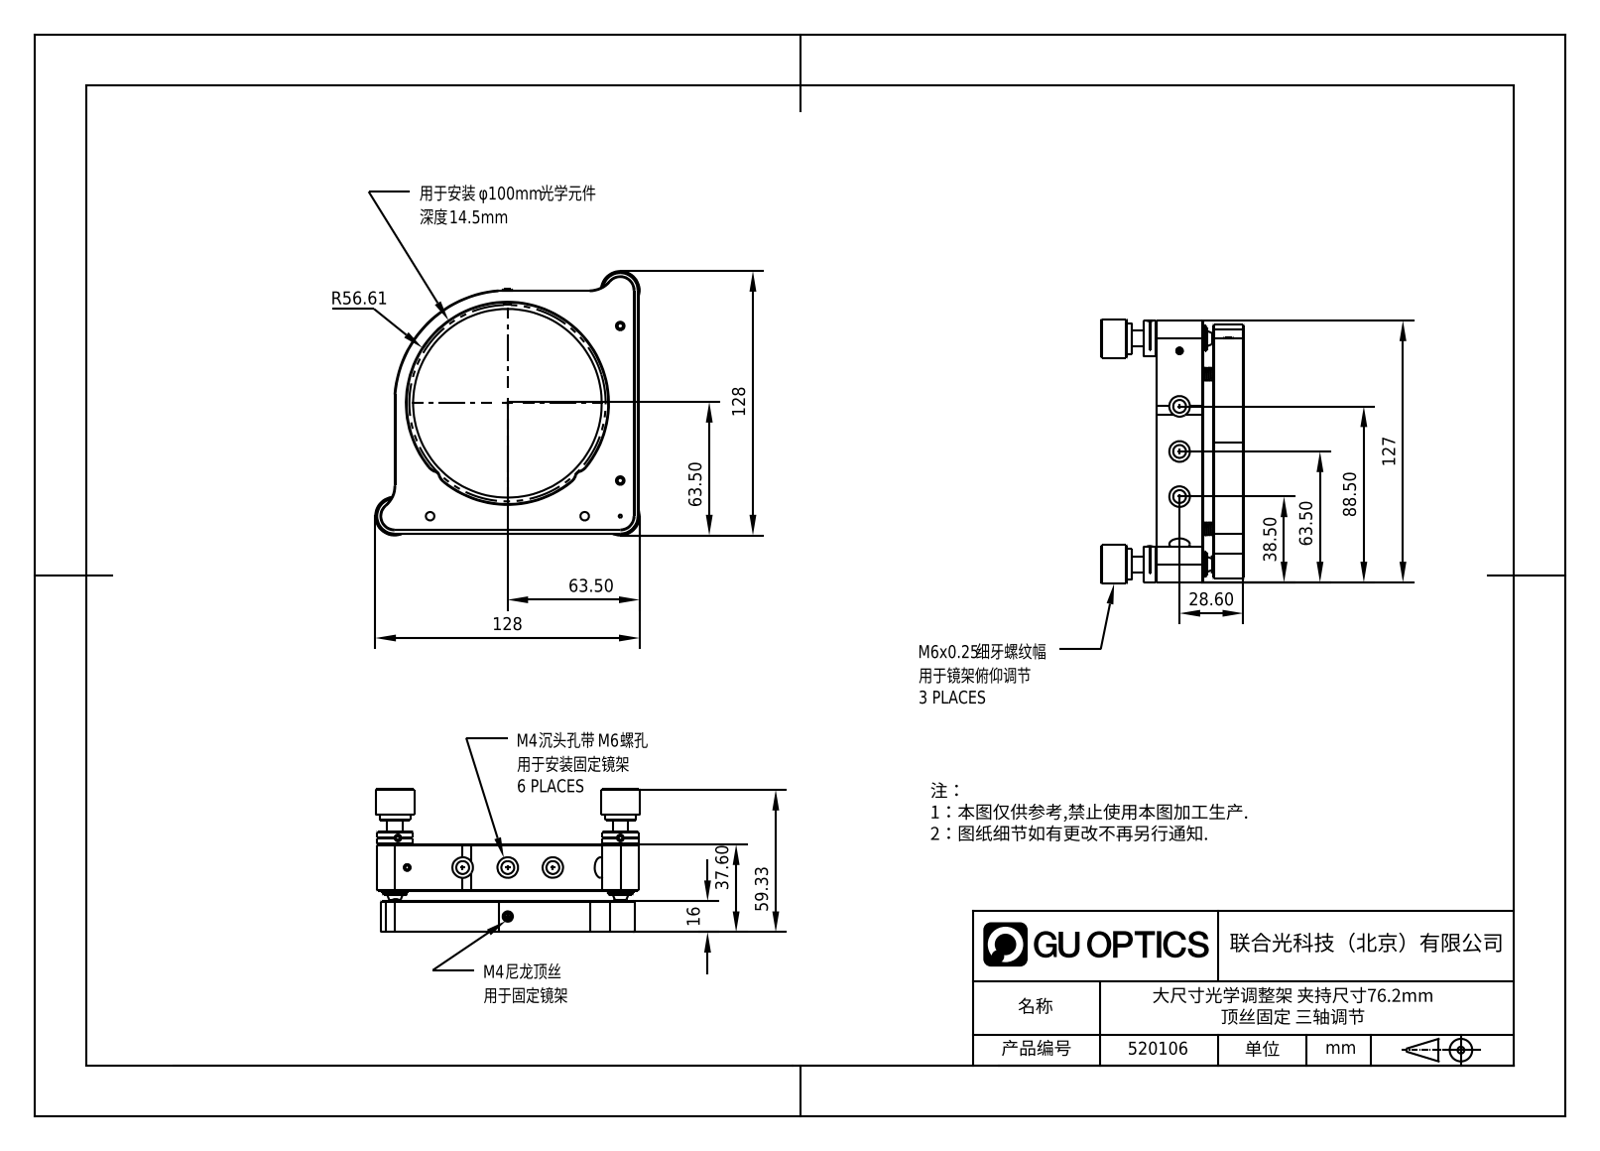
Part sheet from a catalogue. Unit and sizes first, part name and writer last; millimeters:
Units: millimetres
Overall size (bounding box): 128 × 128 × 59.43
Round holes (diameter × count): ⌀5 ×6, ⌀8 ×6, ⌀6.5 ×4, ⌀9.5 ×3, ⌀2.5 ×2
Round bosses / shafts (diameter × count): ⌀3.3 ×6, ⌀3 ×4, ⌀2 ×4, ⌀15 ×3, ⌀14 ×3, ⌀6 ×3, ⌀8 ×2, ⌀102 ×1
Partial cylindrical surfaces — rounded edges, fillets, slot ends (radius × count): R5 ×11, R1.05 ×8, R0.2 ×4, R5.5 ×3, R2.5 ×2, R8 ×2, R10 ×2, R56.61 ×1
Main face-to-face distances: 16, 1.5, 19.6, 18, 21.6, 37.6, 3.6, 118.5, 120, 14
Hole centre spacings: 25, 21.5, 24, 26.75, 50, 51.75, 67.5, 76.75
Bodies: 0 solids, 326 faces (157 planar, 89 cylindrical, 80 other)
Part name (STEP PRODUCT): 520110
STEP written by: SolidWorks 2020 (AUTOMOTIVE_DESIGN)
